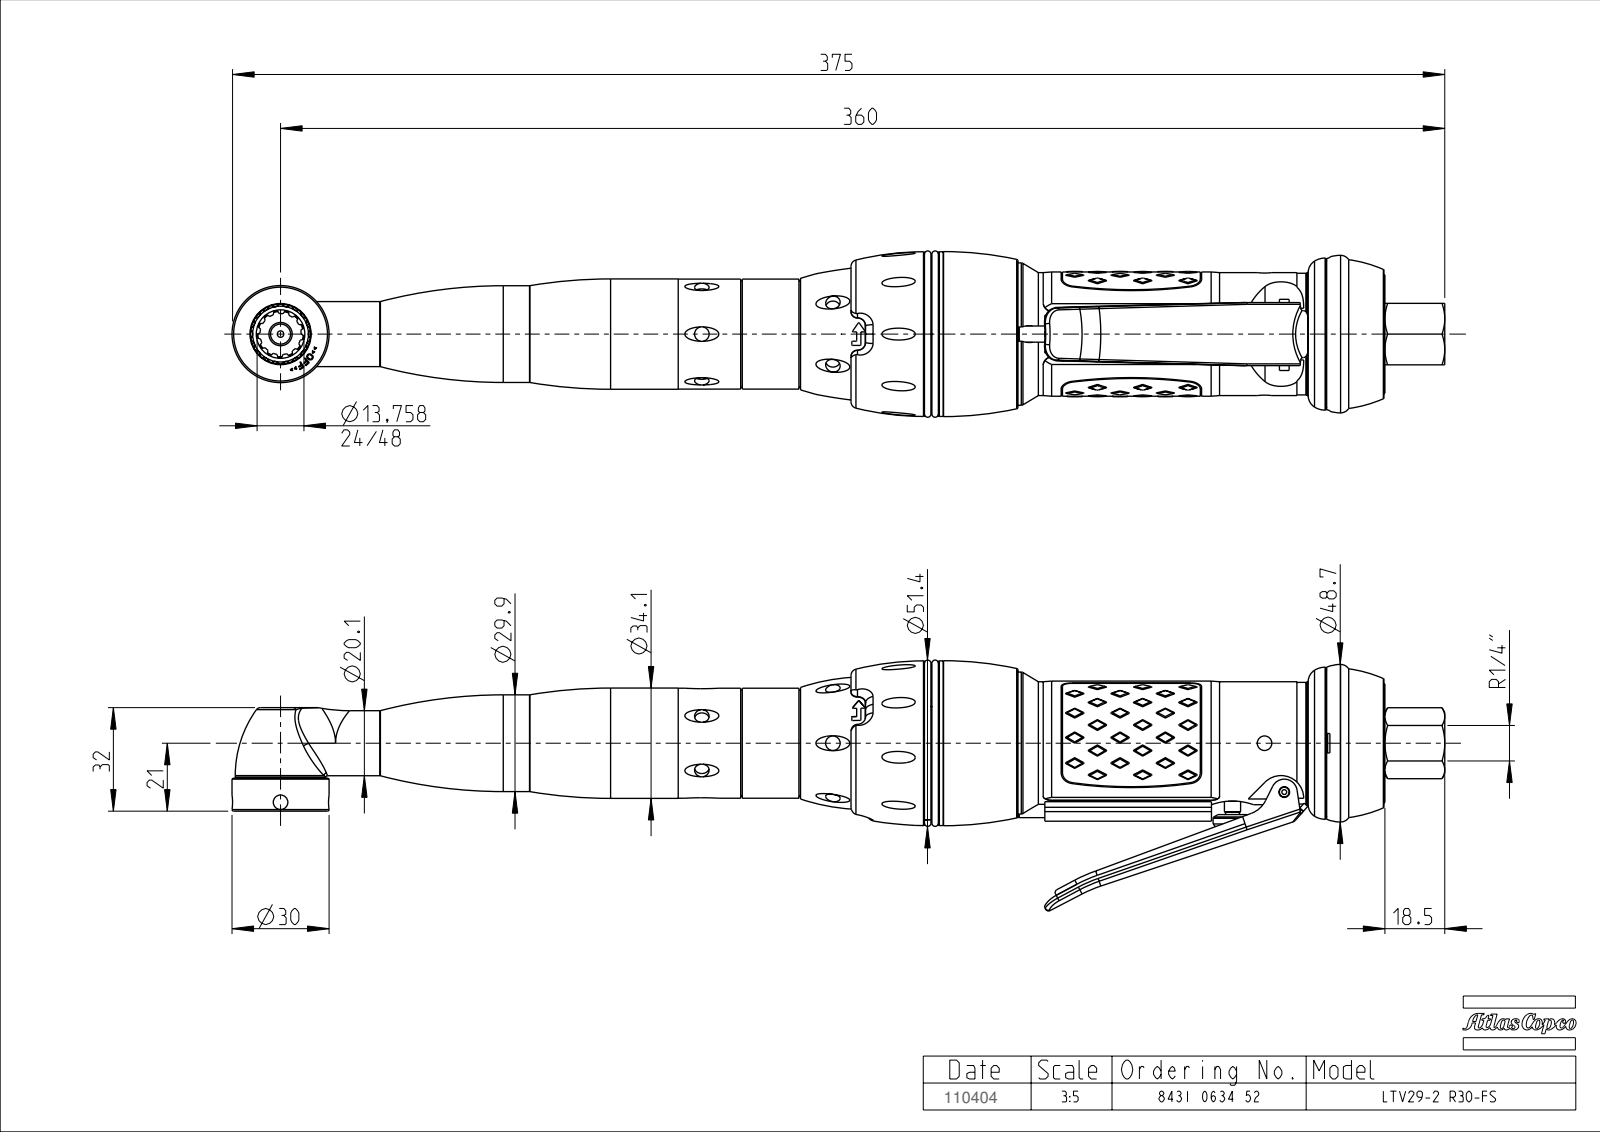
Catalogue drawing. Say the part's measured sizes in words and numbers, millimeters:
The part is named "TMP83141_SW". Its 3-D file was written by "PRO/ENGINEER BY PARAMETRIC TECHNOLOGY CORPORATION, 2008310 (CONFIG_CONTROL_DESIGN)". It is 0 solids with 358 faces: 52 planar, 145 cylindrical and 161 other. Overall it measures 374.8 by 77.55 by 51.4 millimeters. Round holes: 4 of diameter 4.5, 2 of diameter 5.5, 1 of diameter 11, 1 of diameter 15, 1 of diameter 18.9. Round bosses or shafts: 1 of diameter 50.9, 1 of diameter 44, 1 of diameter 38.4, 1 of diameter 38, 1 of diameter 37.6, 1 of diameter 35.8, 1 of diameter 34.1, 1 of diameter 34. Partial cylindrical surfaces (rounded edges, fillets, slot ends): 3 of radius 1, 2 of radius 0.2, 2 of radius 4, 2 of radius 5, 2 of radius 19, 2 of radius 20.5, 1 of radius 6, 1 of radius 6.35. The main face-to-face distances are 19, 3, 19.25, 18.5, 21.5, 32, 19.5, 11.3, 20.7, 4.1. The hole center spacings are 13.5, 21.84.
